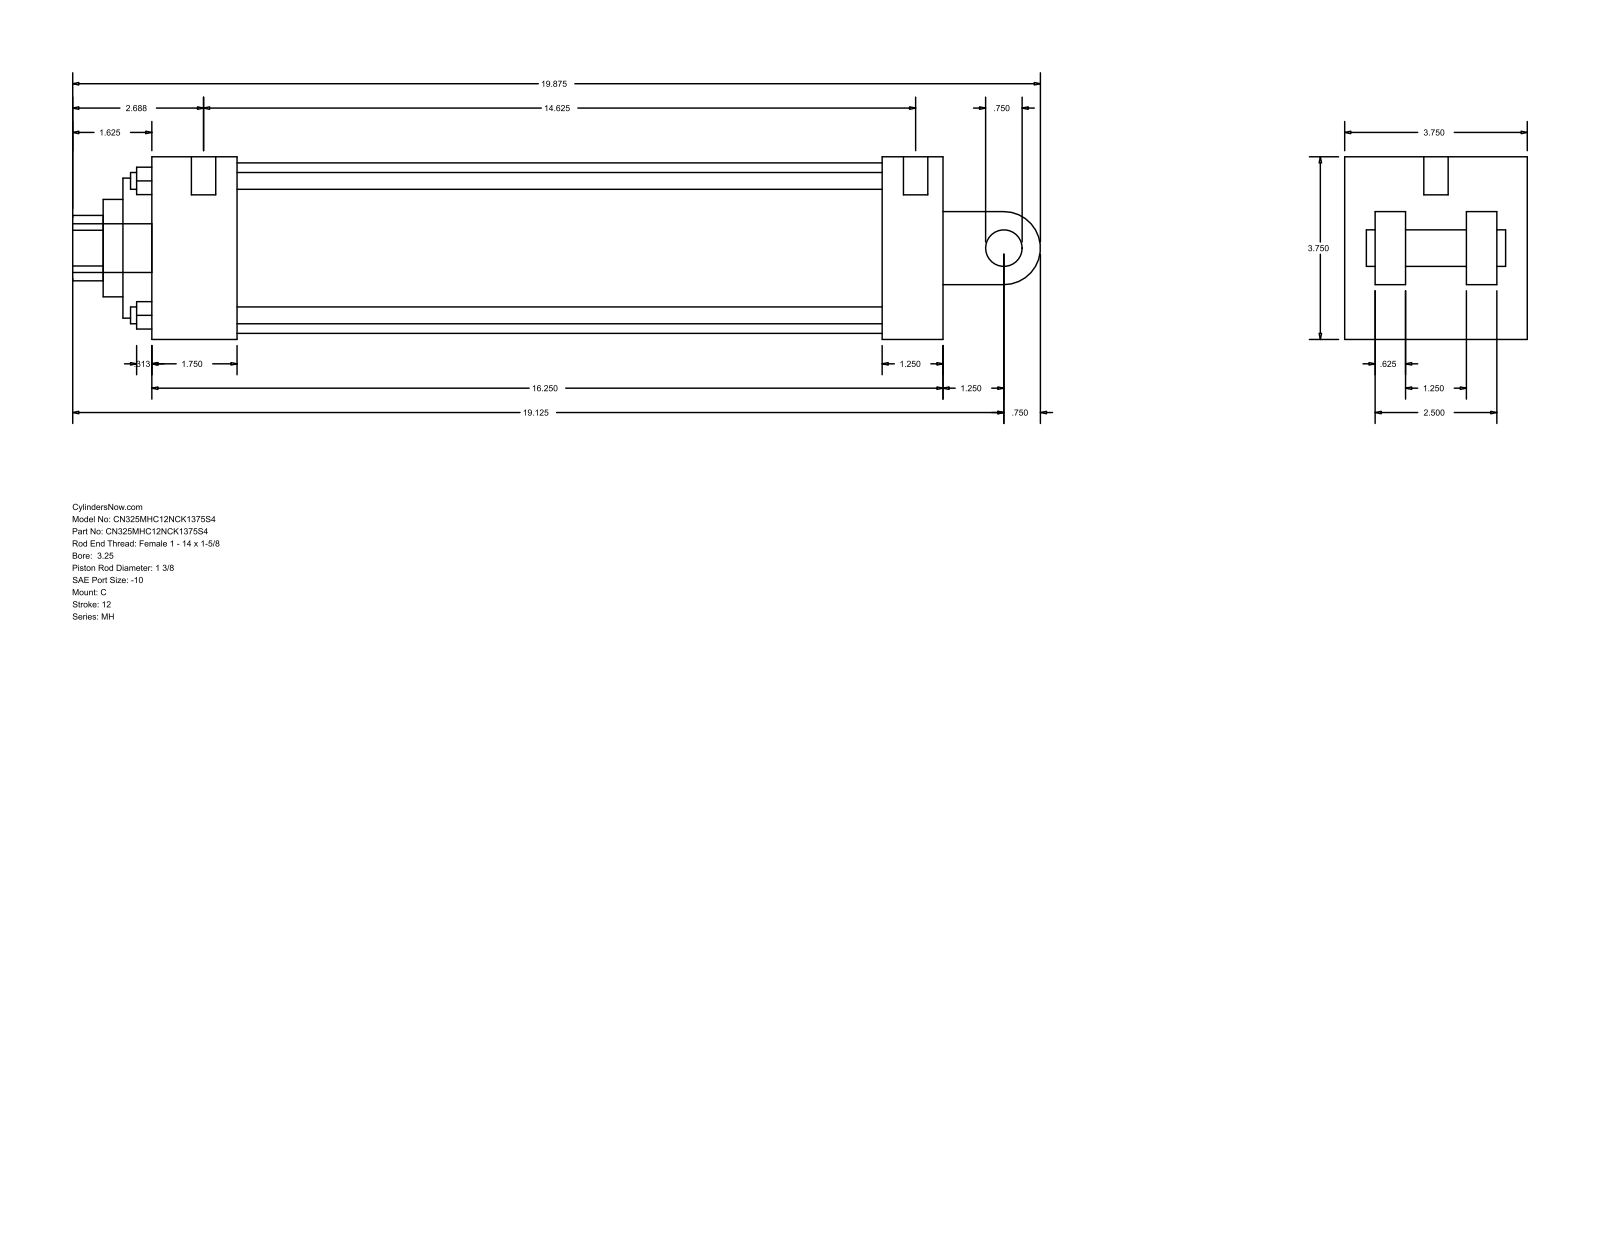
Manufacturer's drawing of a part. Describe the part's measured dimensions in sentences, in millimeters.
The part is named "MH_C__0325_1.375". Its 3-D file was written by "GSSL Pune (CONFIG_CONTROL_DESIGN)". It is 0 solids with 101 faces: 71 planar, 30 cylindrical and 0 other. Overall it measures 504.82 by 95.25 by 95.25 millimeters. Round holes: 4 of diameter 8.76, 2 of diameter 5.56, 1 of diameter 12.7, 1 of diameter 34.92, 1 of diameter 50.8, 1 of diameter 73.03, 1 of diameter 88.9. Round bosses or shafts: 2 of diameter 5.56, 1 of diameter 25.4, 1 of diameter 19.05, 1 of diameter 12.7. Partial cylindrical surfaces (rounded edges, fillets, slot ends): 1 of radius 17.06, 1 of radius 19.05. The main face-to-face distances are 95.24, 15.87, 412.75, 63.5, 79.37, 31.74, 47.63, 44.45, 381, 336.55. The hole center spacings are 49.57, 70.1, 99.14, 4.76.
